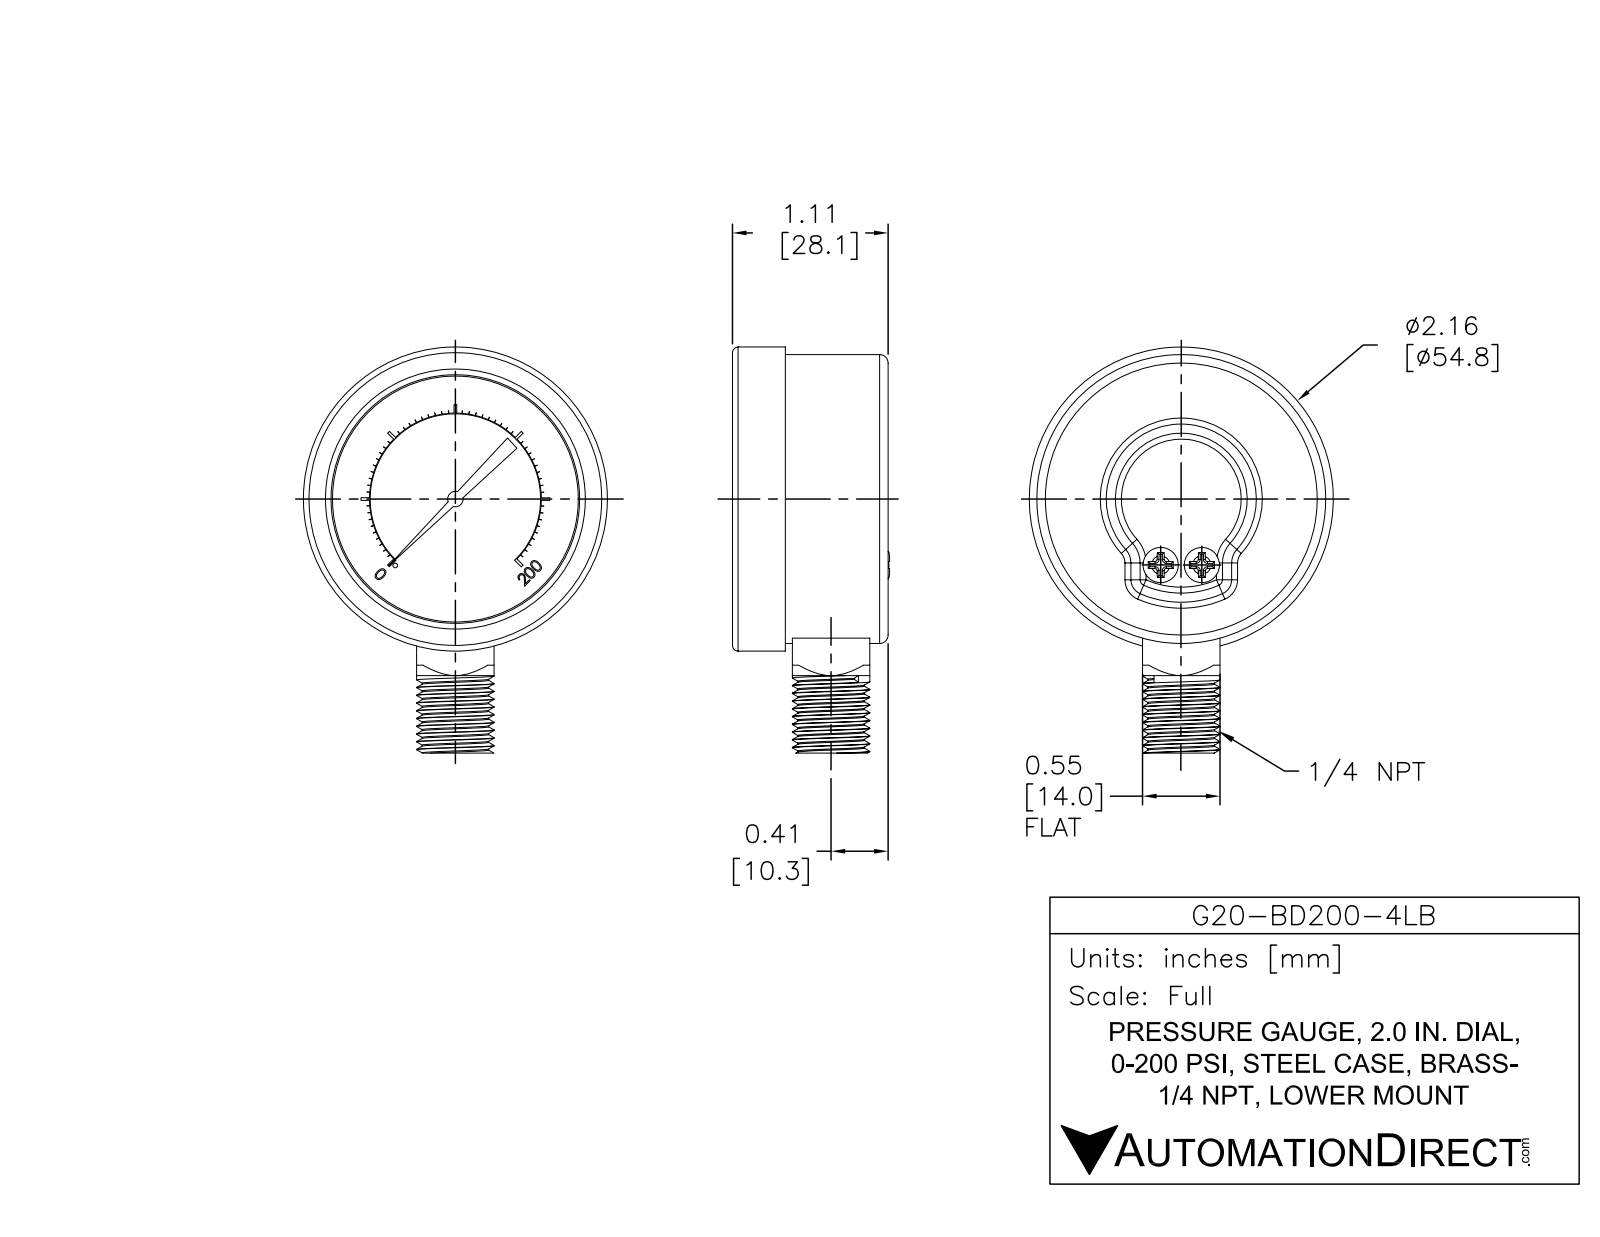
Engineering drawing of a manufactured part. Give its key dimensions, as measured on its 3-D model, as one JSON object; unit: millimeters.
{"part_name": "G20-BD200-4LB", "step_written_by": "SolidWorks 2021 (AUTOMOTIVE_DESIGN)", "units": "millimeters", "bodies": {"solids": 1, "faces": 426, "planar": 274, "cylindrical": 81, "other": 71}, "overall_size": [73.2, 54.8, 28.3], "volume_mm3": 52140, "surface_area_mm2": 11630, "round_holes": [[3.6, 1], [44.3, 1]], "round_bosses_or_shafts": [[6.4, 2], [54.8, 1], [52.1, 1], [14, 1], [2.8, 1], [0.8, 1]], "partial_cylinders_radius": [[1.5, 4], [15.4, 1], [15.5, 1]], "face_to_face_distances": [20.7, 28.1, 7.4, 2.5, 18.2, 25.5, 16, 18.5, 2.2, 9.5]}
